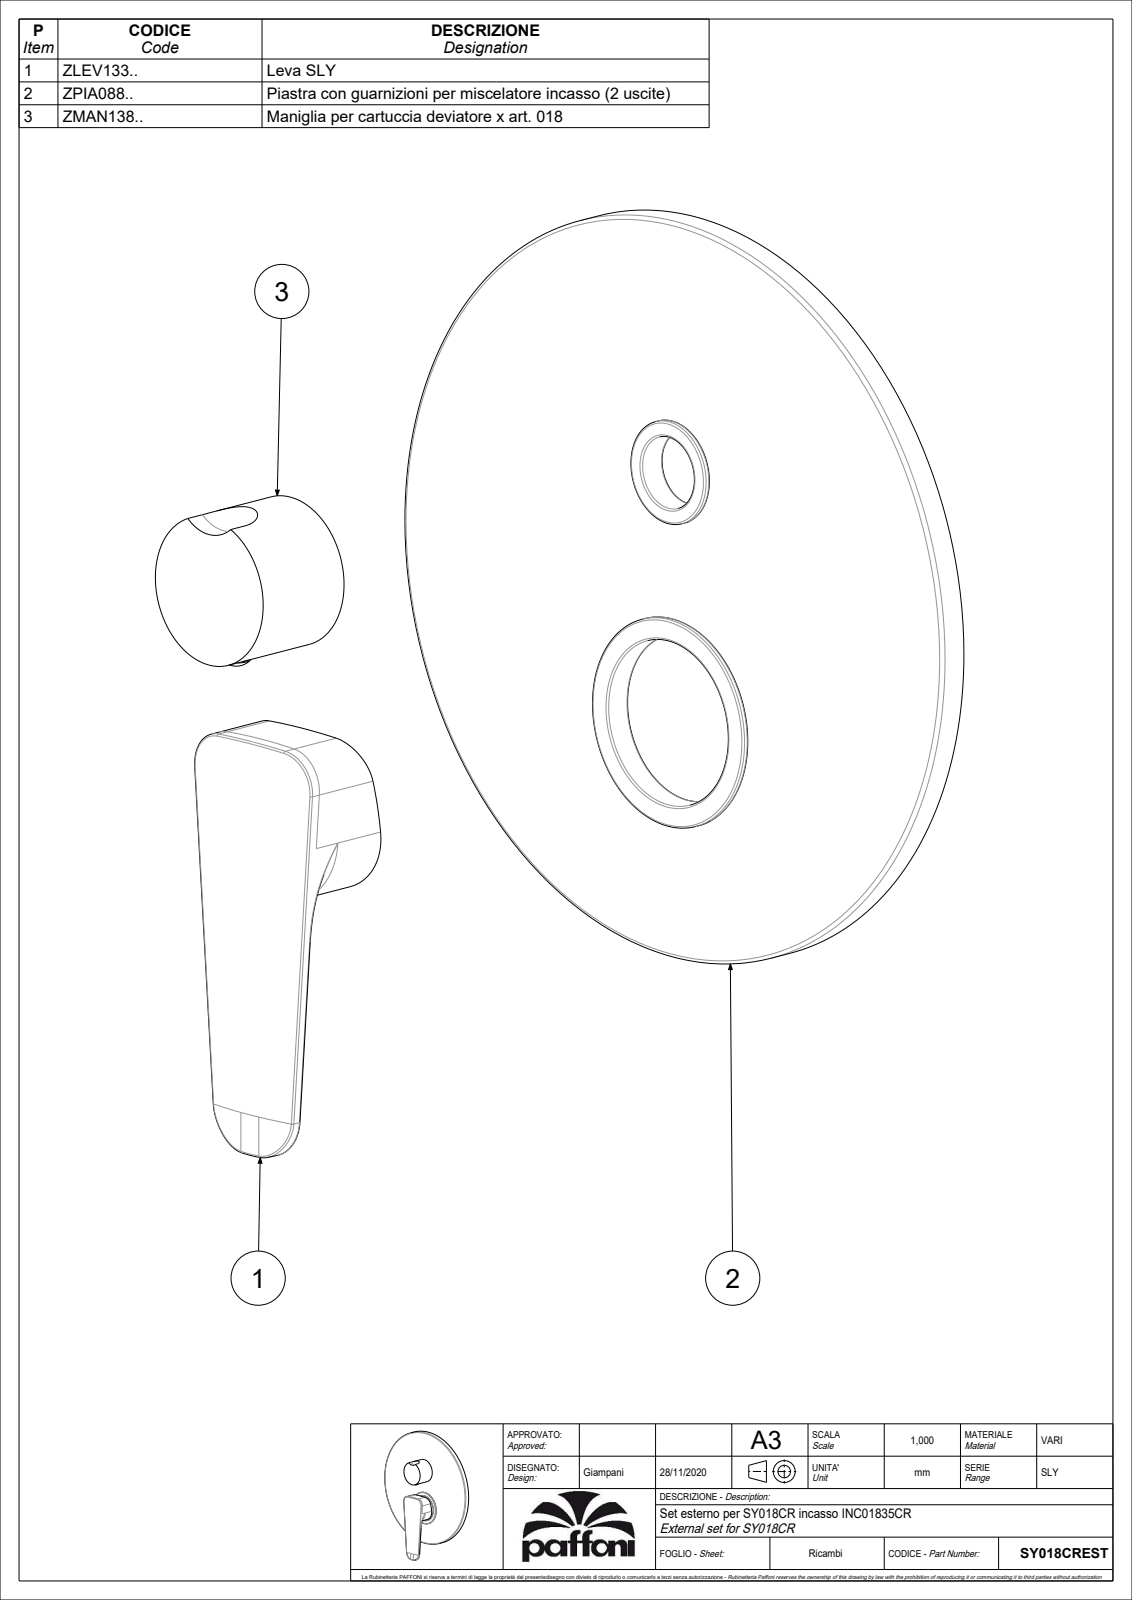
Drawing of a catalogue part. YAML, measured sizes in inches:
part_name: "SY018CREST"
step_written_by: "CREO PARAMETRIC BY PTC INC, 2020044 (CONFIG_CONTROL_DESIGN)"
units: inches
bodies: {solids: 3, faces: 268, planar: 82, cylindrical: 85, other: 101}
overall_size: [8.818, 7.874, 1.628]
volume: 11.77
surface_area: 164.7
round_holes:
  - {diameter: 0.118, count: 2}
  - {diameter: 0.126, count: 1}
  - {diameter: 0.13, count: 1}
  - {diameter: 0.165, count: 1}
  - {diameter: 0.177, count: 1}
  - {diameter: 0.583, count: 1}
  - {diameter: 0.752, count: 1}
  - {diameter: 1.417, count: 1}
  - {diameter: 1.756, count: 1}
  - {diameter: 1.969, count: 1}
  - {diameter: 5.709, count: 1}
  - {diameter: 7.795, count: 1}
round_bosses_or_shafts:
  - {diameter: 0.299, count: 2}
  - {diameter: 0.217, count: 2}
  - {diameter: 0.197, count: 2}
  - {diameter: 7.874, count: 1}
  - {diameter: 7.677, count: 1}
  - {diameter: 2.213, count: 1}
  - {diameter: 1.965, count: 1}
  - {diameter: 1.575, count: 1}
partial_cylinders:
  - {radius: 0.059, count: 4}
  - {radius: 0.394, count: 2}
  - {radius: 0.177, count: 1}
  - {radius: 0.492, count: 1}
  - {radius: 0.814, count: 1}
  - {radius: 4.42, count: 1}
  - {radius: 7.874, count: 1}
face_to_face_distances: [0.039, 0.315, 0.354, 0.433, 1.437, 1.122, 1.083, 0.079, 0.118, 1.004]
hole_center_spacings: [0.228, 0.394, 1.268, 1.409, 1.661, 2.677, 3.071]
